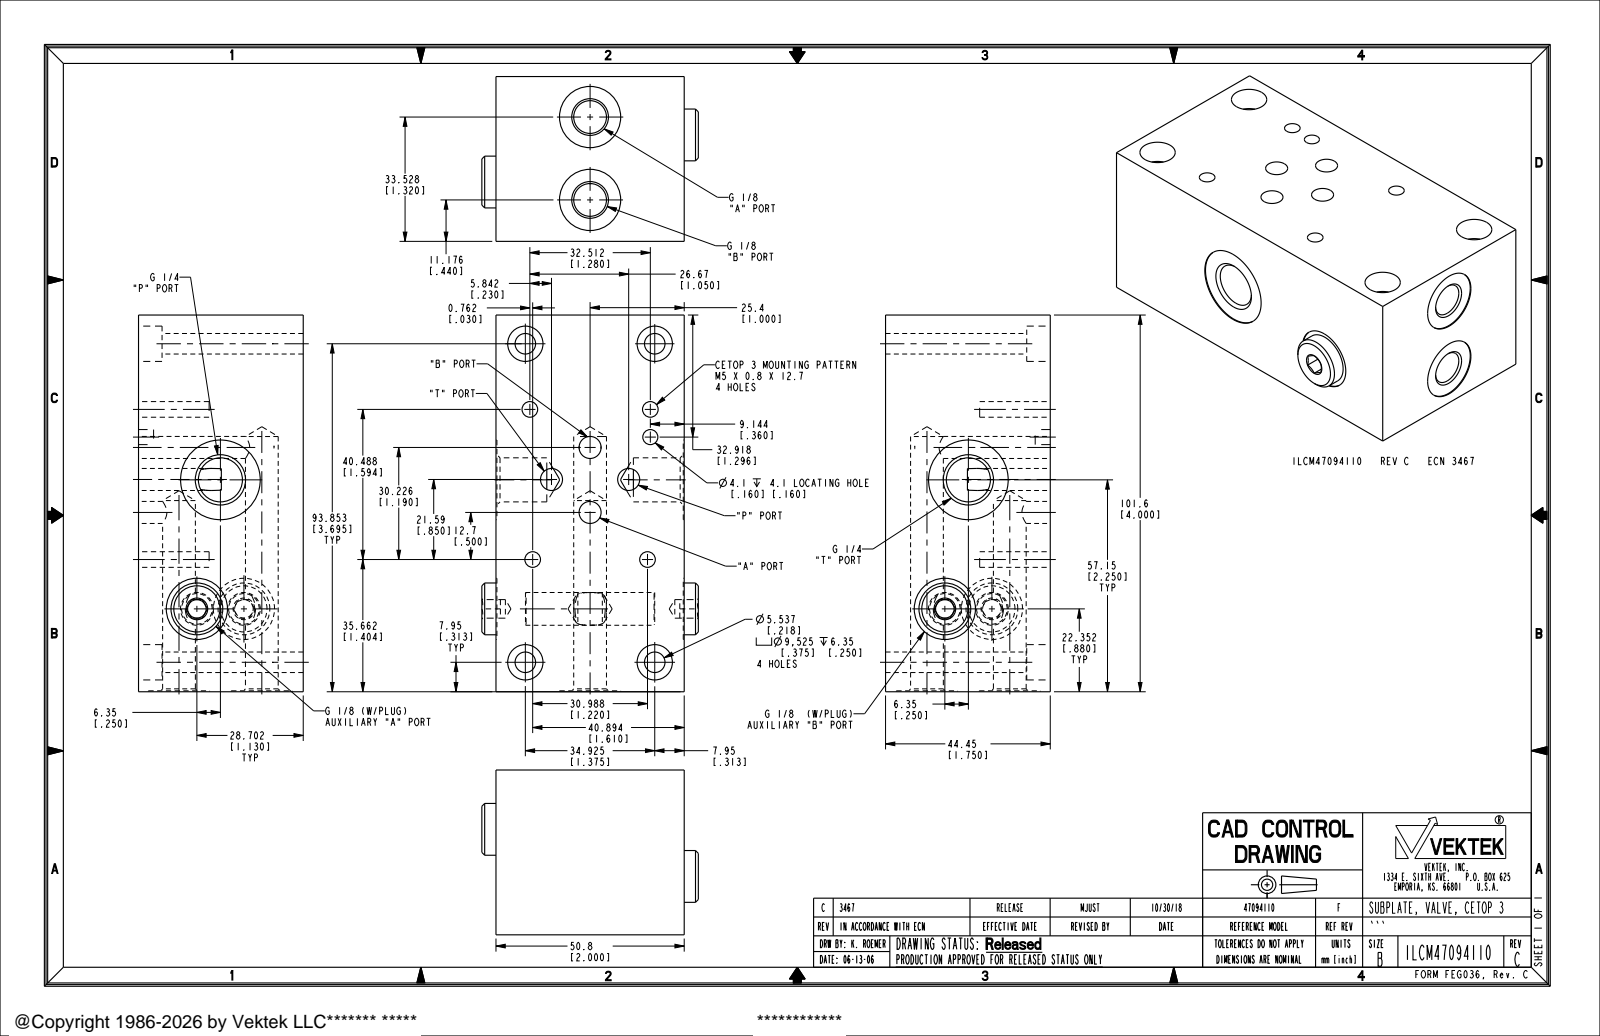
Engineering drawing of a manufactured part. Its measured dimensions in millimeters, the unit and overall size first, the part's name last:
Units: millimetres
Overall size (bounding box): 101.6 × 58.42 × 44.45
Round holes (diameter × count): ⌀4.22 ×4, ⌀5.54 ×4, ⌀5.94 ×4, ⌀8.84 ×4, ⌀9.53 ×4, ⌀16.51 ×4, ⌀5 ×2, ⌀4.06 ×1, ⌀11.89 ×1, ⌀21.49 ×1
Round bosses / shafts (diameter × count): ⌀13.97 ×2
Main face-to-face distances: 44.45, 50.8, 101.6, 50.55, 50.3, 101.35, 4.06, 3.81, 54.36, 54.61
Hole centre spacings: 13.53, 13.69, 17.74, 19.23, 19.78, 20.03, 22.18, 27.78
Volume: 208 248 mm³ · Surface area: 35 317 mm²
Bodies: 1 solid, 155 faces (53 planar, 68 cylindrical, 34 other)
Part name (STEP PRODUCT): ILCM47094110
STEP written by: PRO/ENGINEER BY PARAMETRIC TECHNOLOGY CORPORATION, 2013320 (AUTOMOTIVE_DESIGN)
